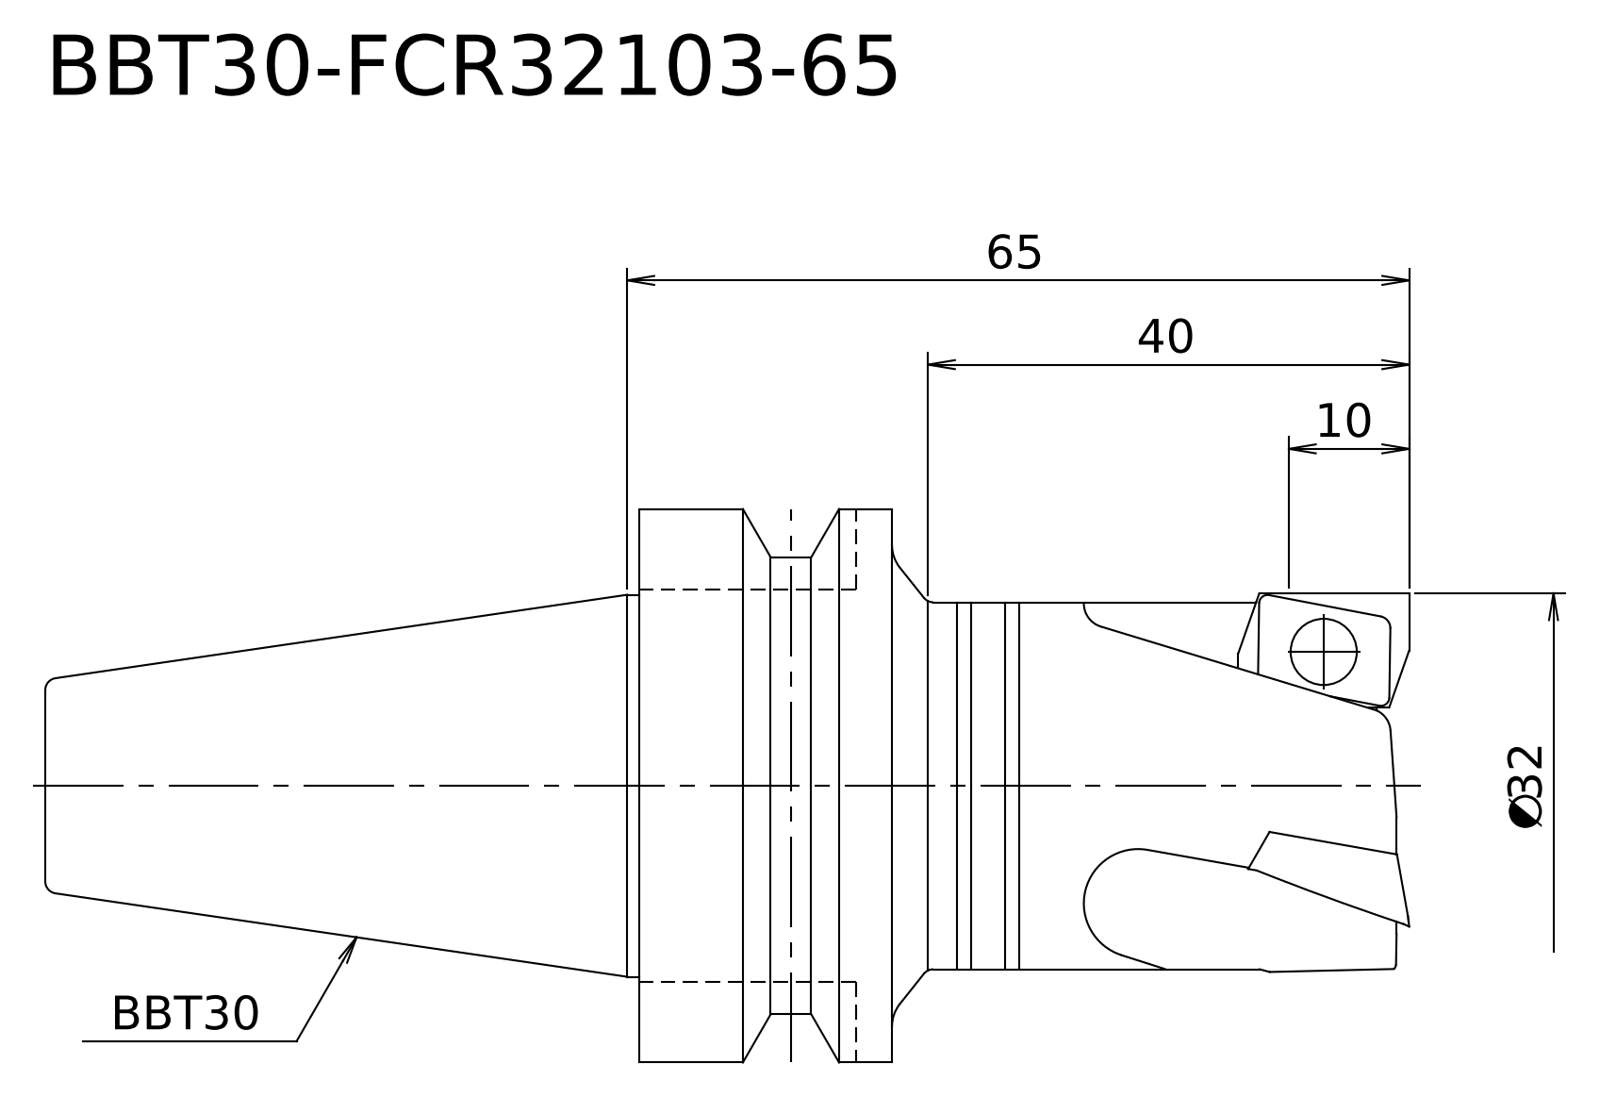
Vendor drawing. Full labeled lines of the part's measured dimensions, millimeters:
STEP written by: Kubotek KeyCreator V8.5.1 (14335) (CONFIG_CONTROL_DESIGN)
Units: millimetres
Bodies: 1 solid, 17 faces (4 planar, 6 cylindrical, 7 other)
Overall size (bounding box): 113.4 × 46 × 46
Volume: 89 317 mm³ · Surface area: 14 235 mm²
Round bosses / shafts (diameter × count): ⌀46 ×1, ⌀38 ×1, ⌀32 ×1, ⌀31.75 ×1, ⌀30.5 ×1
Main face-to-face distances: 64, 43, 21, 113.4, 70.4, 49.4
